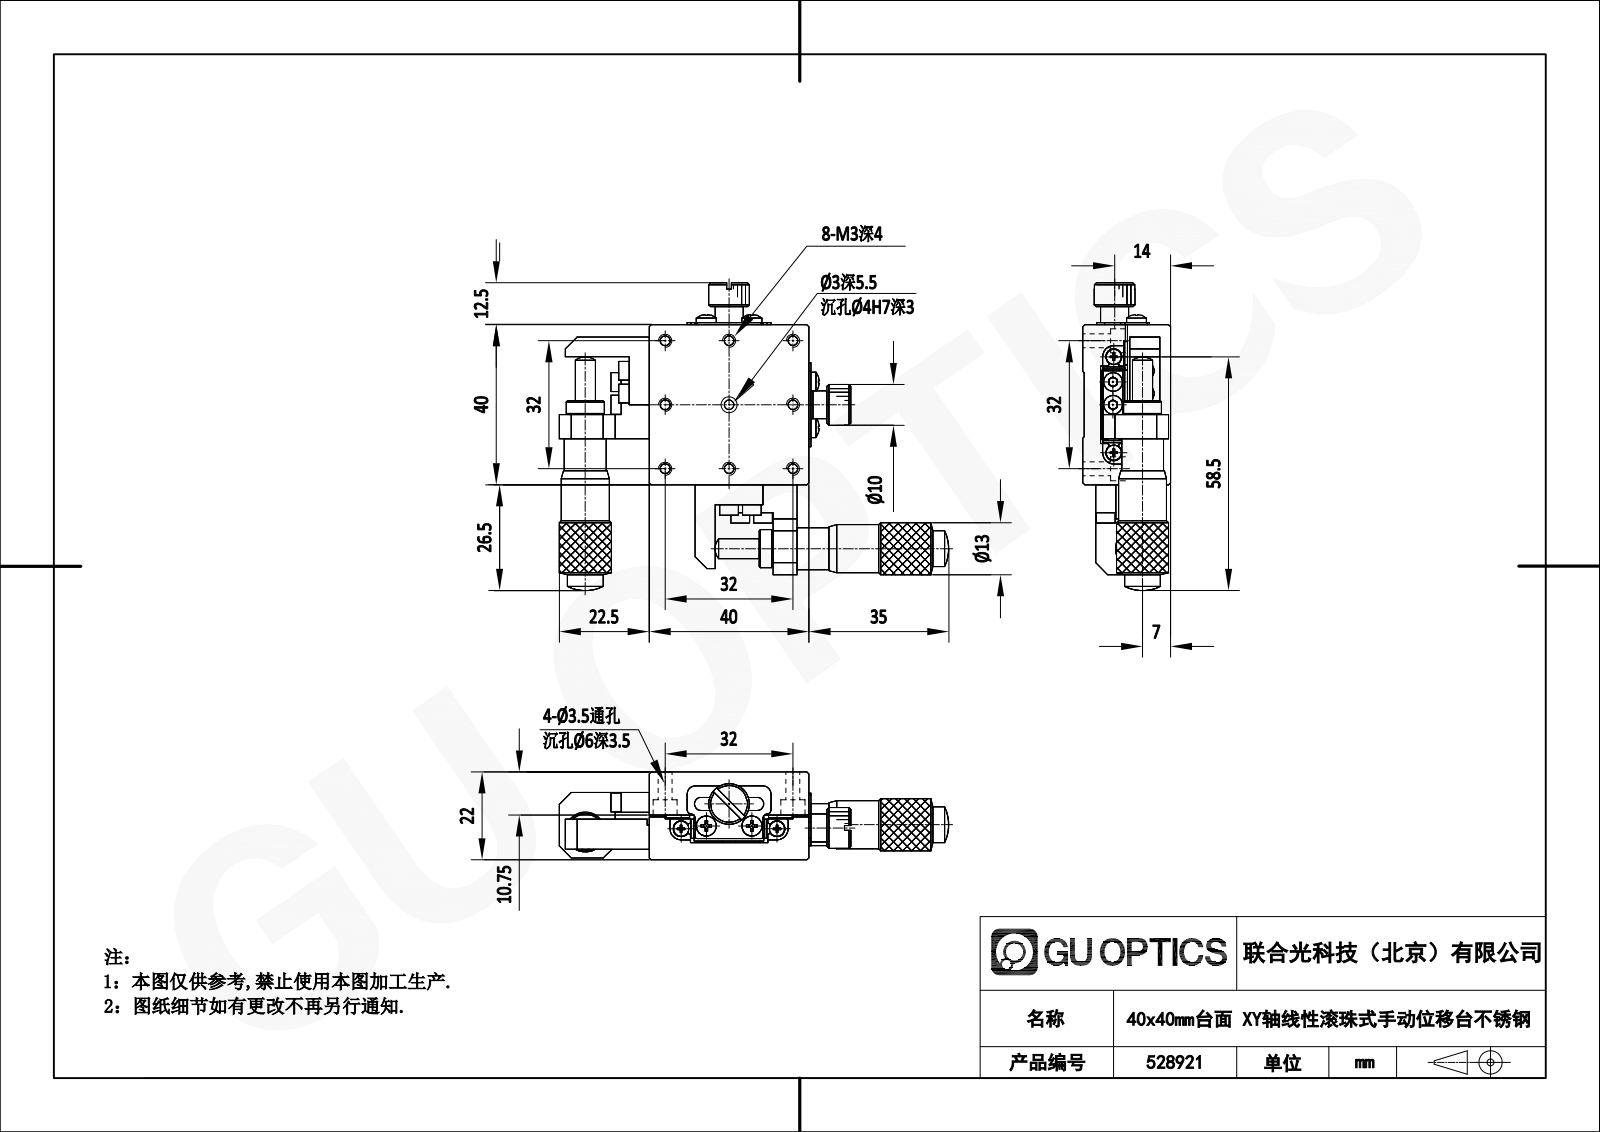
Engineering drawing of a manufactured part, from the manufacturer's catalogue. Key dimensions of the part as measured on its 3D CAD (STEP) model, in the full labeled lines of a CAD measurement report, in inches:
Part name (STEP PRODUCT): 528921
STEP written by: SolidWorks 2020 (CONFIG_CONTROL_DESIGN)
Units: inches
Bodies: 0 solids, 4551 faces (483 planar, 1028 cylindrical, 3040 other)
Overall size (bounding box): 3.859 × 3.091 × 1.003
Round holes (diameter × count): ⌀0.11 ×6, ⌀0.081 ×4, ⌀0.118 ×4, ⌀0.276 ×2, ⌀0.353 ×1, ⌀0.353 ×1
Round bosses / shafts (diameter × count): ⌀0.097 ×8, ⌀0.236 ×6, ⌀0.081 ×6, ⌀0.138 ×4, ⌀0.063 ×4, ⌀0.513 ×2, ⌀0.474 ×2, ⌀0.472 ×2
Partial cylindrical surfaces — rounded edges, fillets, slot ends (radius × count): R0.02 ×8, R0.039 ×4, R0.069 ×4, R0.083 ×3, R0.197 ×2
Main face-to-face distances: 0.201, 0.453, 0.213, 1.575, 0.413, 0.441, 0.039, 0.02, 0.205, 0.654
Hole centre spacings: 0.236, 0.392, 0.378, 0.396, 0.472, 0.515, 0.142, 0.363
